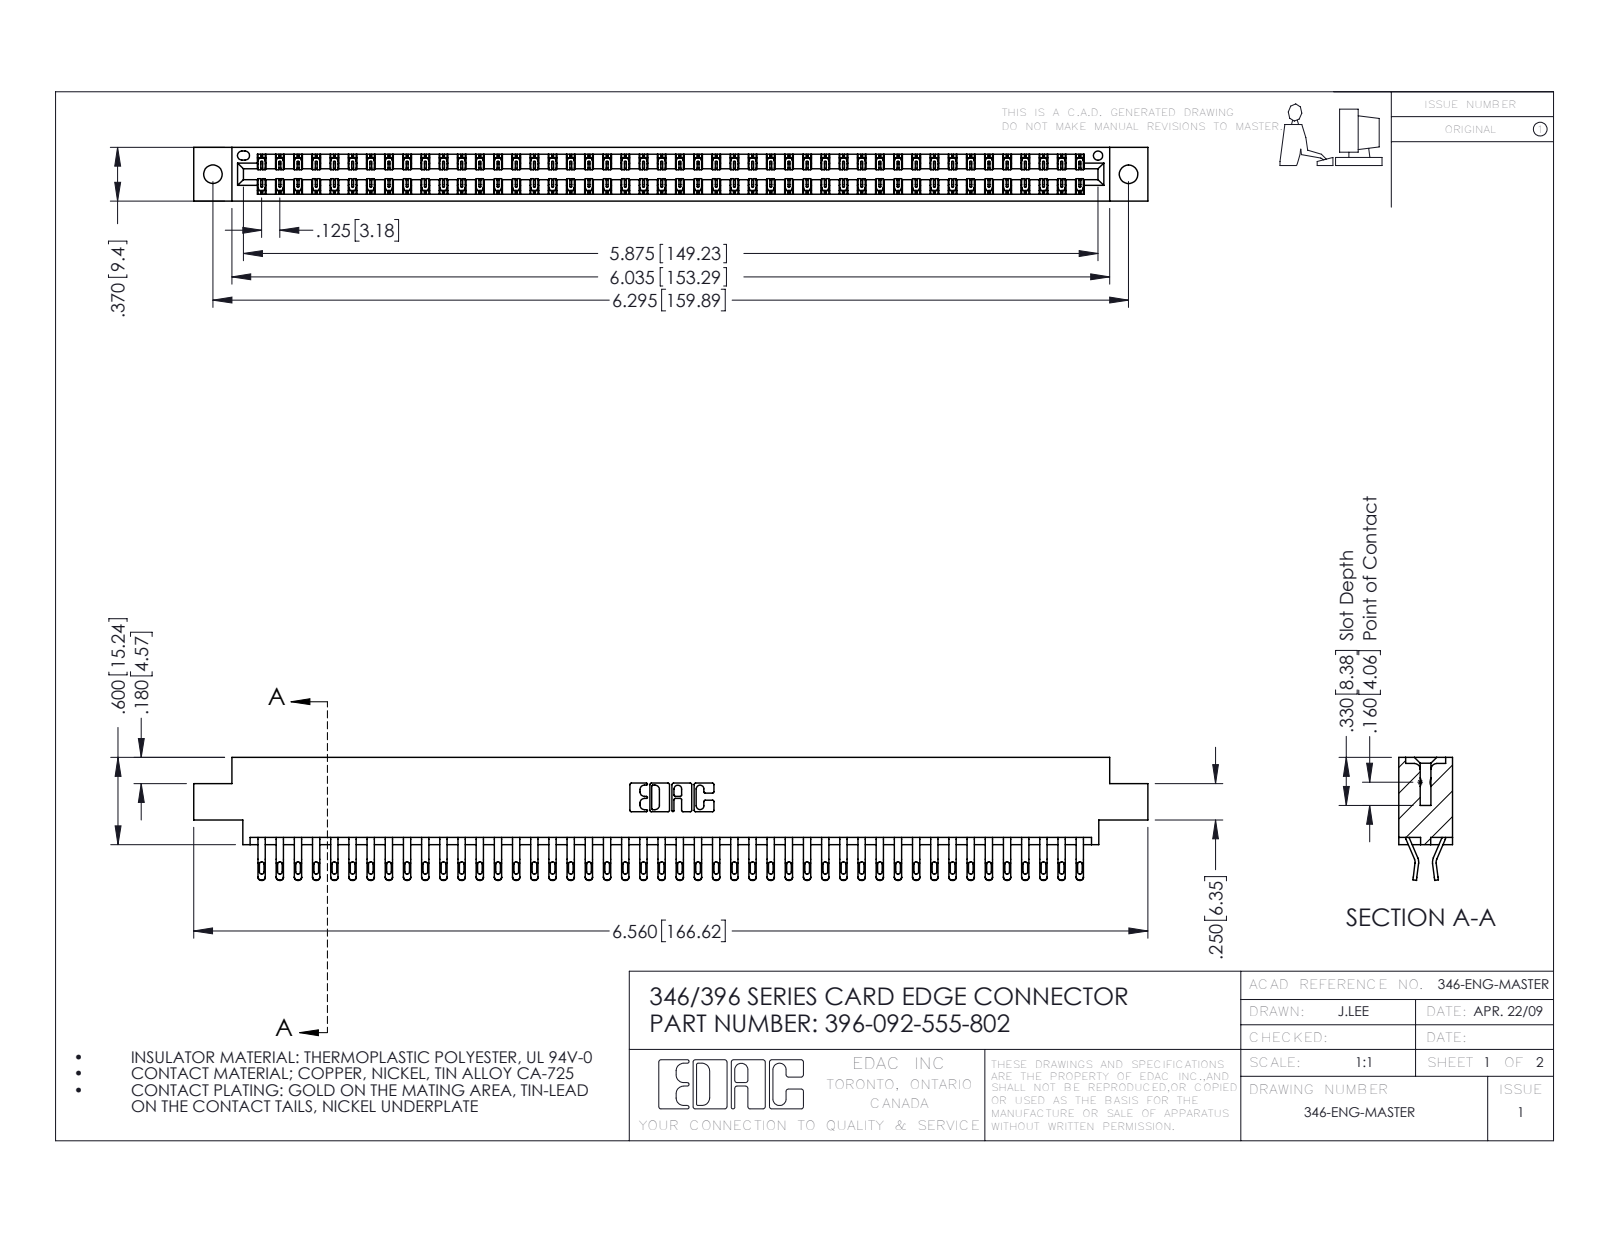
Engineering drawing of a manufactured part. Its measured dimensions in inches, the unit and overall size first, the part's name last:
Units: inches
Overall size (bounding box): 6.56 × 0.845 × 0.37
Round holes (diameter × count): ⌀0.128 ×2, ⌀0.064 ×1
Partial cylindrical surfaces — rounded edges, fillets, slot ends (radius × count): R0.016 ×184, R0.02 ×184, R0.006 ×138, R0.01 ×22, R0.007 ×6, R0.031 ×6, R0.026 ×3, R0.01 ×2
Main face-to-face distances: 0.048, 0.322, 0.37, 0.25, 0.025, 0.072, 0.298, 0.275, 0.148, 0.222
Hole centre spacings: 0.246, 6.086, 6.295
Volume: 0.998 in³ · Surface area: 36.28 in²
Bodies: 93 solids, 5462 faces (3116 planar, 2346 cylindrical, 0 other)
Part name (STEP PRODUCT): 346 Part_0.170 Offset - 0.128 Dia; 345-292-001_555 Tail; 396-092-555-802
STEP written by: SolidWorks 2016 (CONFIG_CONTROL_DESIGN)
